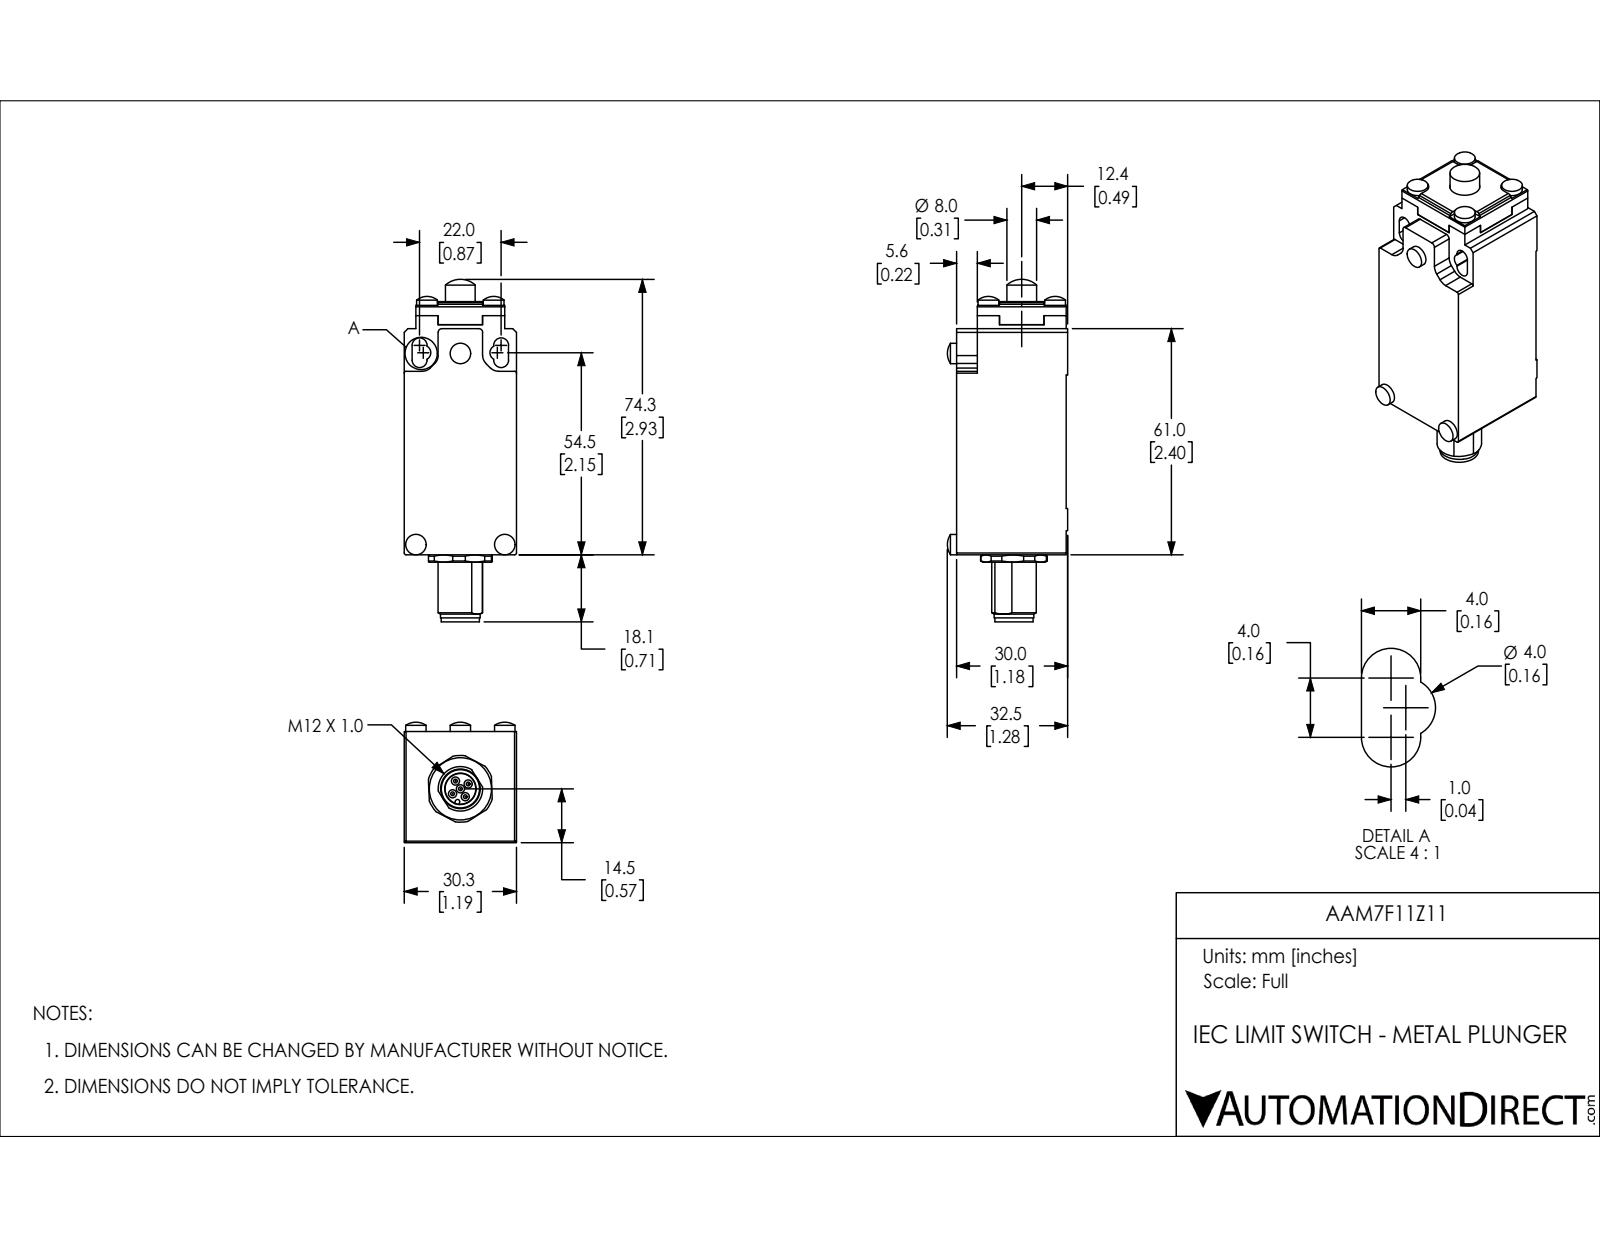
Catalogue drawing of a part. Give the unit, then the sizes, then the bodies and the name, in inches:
Units: inches
Overall size (bounding box): 3.638 × 1.28 × 1.193
Round holes (diameter × count): ⌀0.087 ×5, ⌀0.319 ×1, ⌀0.512 ×1, ⌀0.551 ×1, ⌀0.63 ×1
Round bosses / shafts (diameter × count): ⌀0.055 ×5, ⌀0.039 ×5, ⌀0.22 ×4, ⌀0.217 ×3, ⌀0.421 ×1, ⌀0.406 ×1, ⌀0.315 ×1
Partial cylindrical surfaces — rounded edges, fillets, slot ends (radius × count): R0.039 ×10, R0.118 ×8, R0.079 ×6, R0.02 ×4, R0.024 ×1, R0.236 ×1, R0.354 ×1, R0.394 ×1
Main face-to-face distances: 1.193, 1.165, 0.016, 1.181, 2.444, 0.945, 0.236, 2.445, 0.039, 2.689
Hole centre spacings: 0.098, 0.139, 0.196, 0.052, 0.083, 0.089, 0.159, 0.174
Volume: 3.609 in³ · Surface area: 23.84 in²
Bodies: 4 solids, 282 faces (115 planar, 126 cylindrical, 41 other)
Part name (STEP PRODUCT): AAM7F11Z11
STEP written by: SolidWorks 2018 (AUTOMOTIVE_DESIGN)
